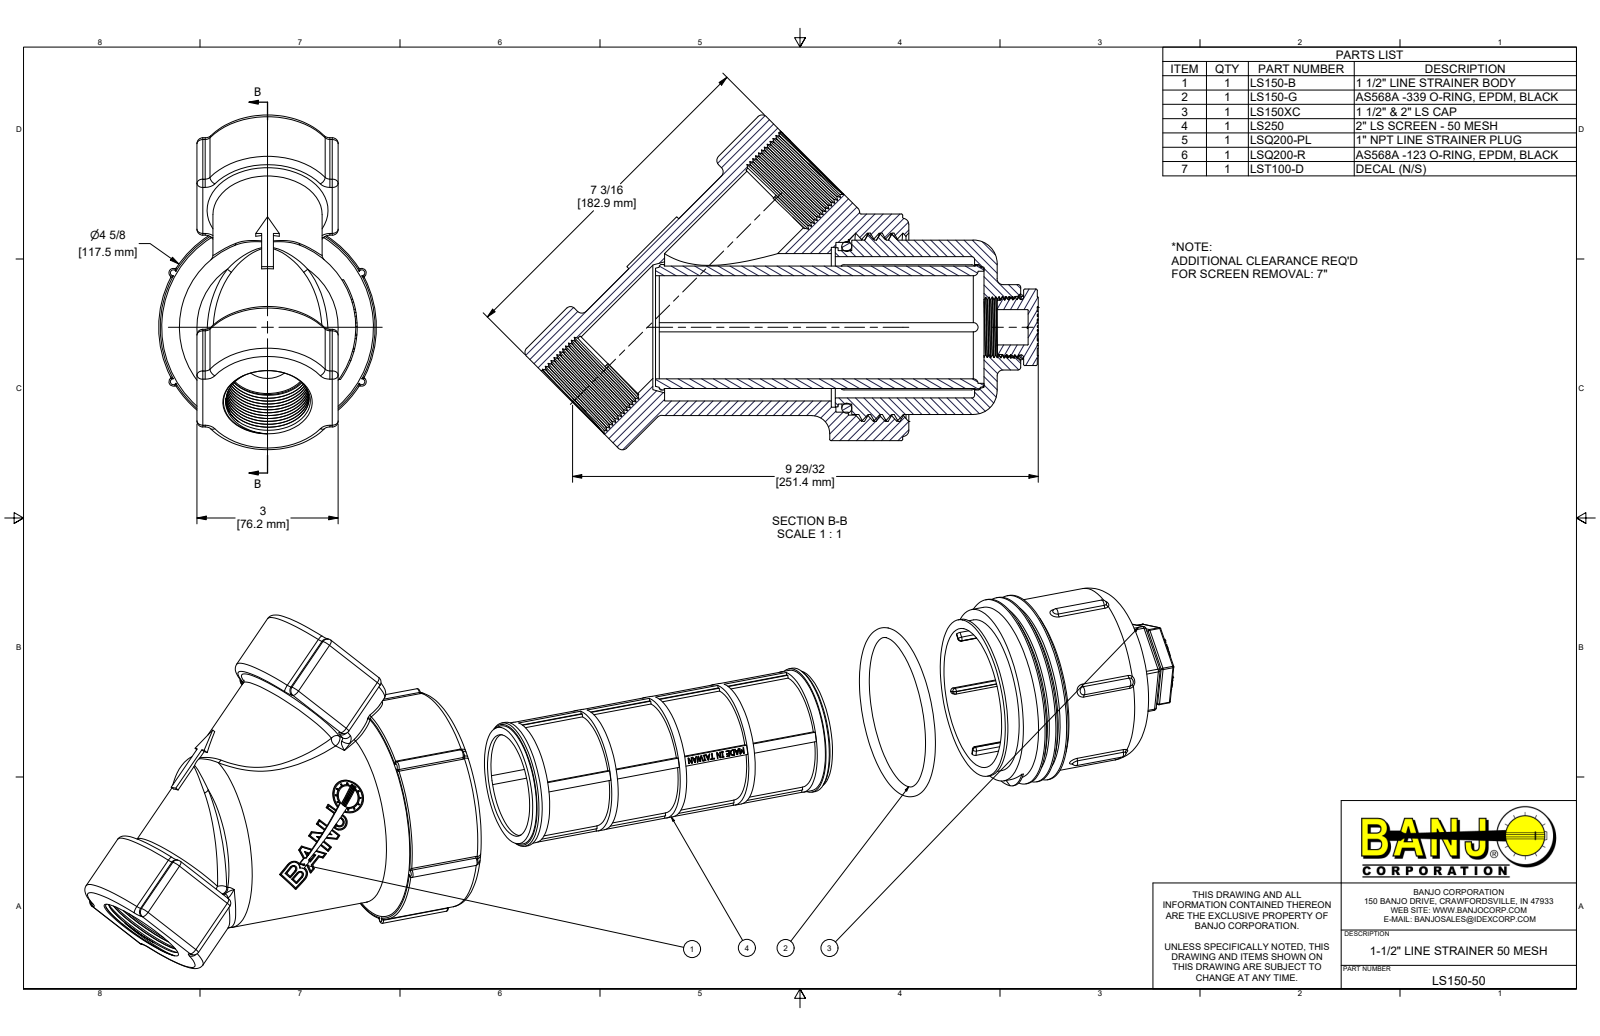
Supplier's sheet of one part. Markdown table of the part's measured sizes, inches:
| quantity | value |
| --- | --- |
| part name | LS150-B; LS150XC; LSQ200-PL; LSQ200-R (+4 more) |
| STEP written by | Autodesk Inventor 2016 (AUTOMOTIVE_DESIGN) |
| units | inches |
| bodies | 5 solids, 1545 faces (709 planar, 266 cylindrical, 570 other) |
| overall size | 10.905 × 7.102 × 4.625 |
| volume | 58.86 in³ |
| surface area | 483.5 in² |
| round holes (diameter × count) | 1.7 × 2, 1.761 × 2, 0.454 × 1, 0.641 × 1, 0.75 × 1, 2.19 × 1, 2.35 × 1, 3 × 1, 3.13 × 1, 3.395 × 1, 3.605 × 1, 3.73 × 1 |
| round bosses / shafts (diameter × count) | 4.625 × 1, 4 × 1, 3.75 × 1, 3.702 × 1, 3.38 × 1, 3.257 × 1, 2.666 × 1, 2.6 × 1 |
| partial cylindrical surfaces (radius × count) | 0.06 × 46, 0.125 × 35, 0.03 × 30, 0.094 × 12, 0.1 × 4, 0.12 × 3, 0.065 × 2, 0.082 × 2 |
| main face-to-face distances | 1.745, 3, 7.189, 3.16, 1.595, 2.785, 1.445, 1.34, 0.2, 1.465 |
